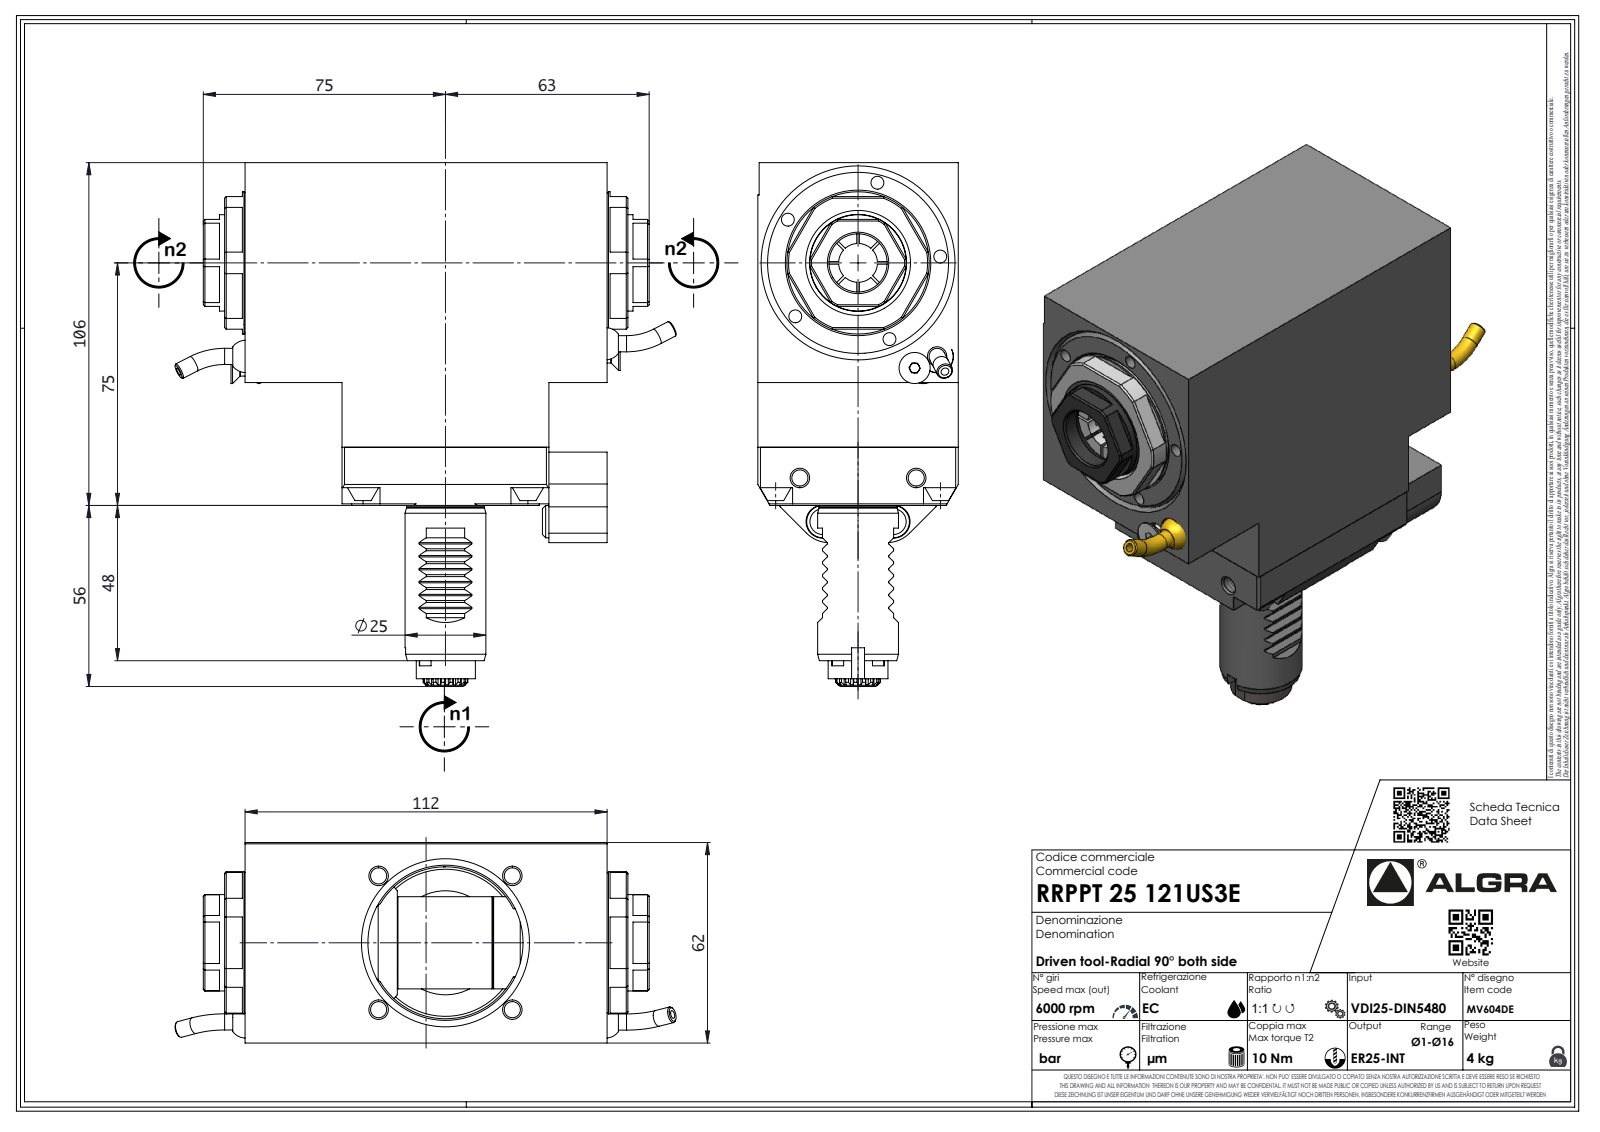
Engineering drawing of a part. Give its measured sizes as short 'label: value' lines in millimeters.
name: RRPPT25121US3E
written by: SolidWorks 2016 (AUTOMOTIVE_DESIGN)
unit: mm
bodies: 7 solids, 964 faces (497 planar, 217 cylindrical, 250 other)
size: 182.28 × 160 × 54.27
volume: 557 124 mm³; area: 56 666 mm²
holes: 2× ⌀3, 1× ⌀2.1, 1× ⌀22.5, 1× ⌀26.38
bosses: 3× ⌀6, 2× ⌀8.5, 1× ⌀40, 1× ⌀34.8, 1× ⌀25, 1× ⌀24.1, 1× ⌀17, 1× ⌀8
rounds: 32× R5.57, 24× R1.49, 12× R0.3, 12× R2, 7× R0.33, 7× R0.52, 7× R3.7, 4× R10
face distances: 54, 60, 103, 110, 43, 0.4, 53.6, 75, 35, 15
hole spacings: 30.41
